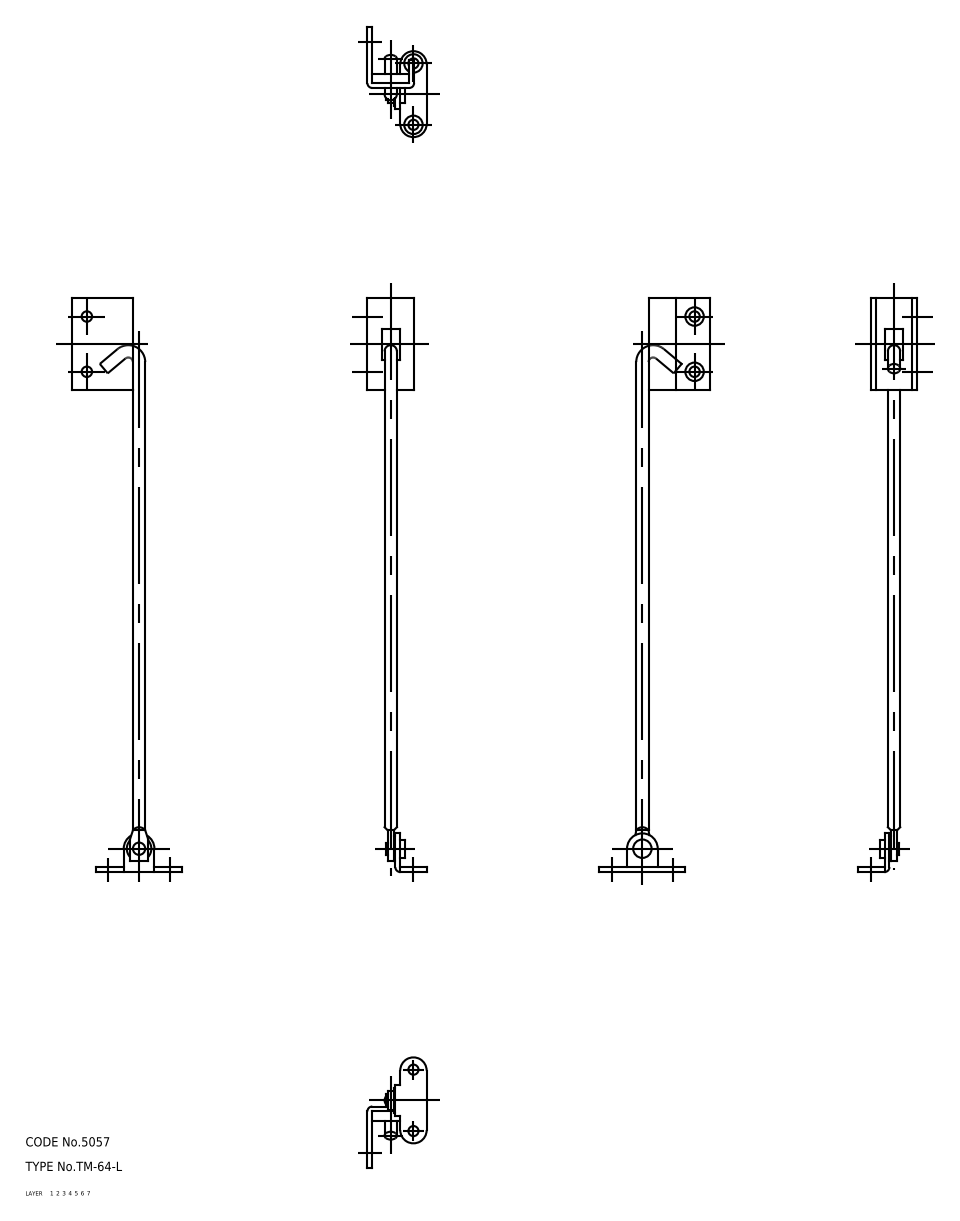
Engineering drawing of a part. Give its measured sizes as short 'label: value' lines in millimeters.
name: washer; stopper; rivet; cushion (+3 more)
written by: CADfix (AUTOMOTIVE_DESIGN)
unit: mm
bodies: 6 solids, 91 faces (0 planar, 0 cylindrical, 91 other)
size: 186.93 × 36 × 19.3
volume: 5 475 mm³; area: 6 841 mm²
